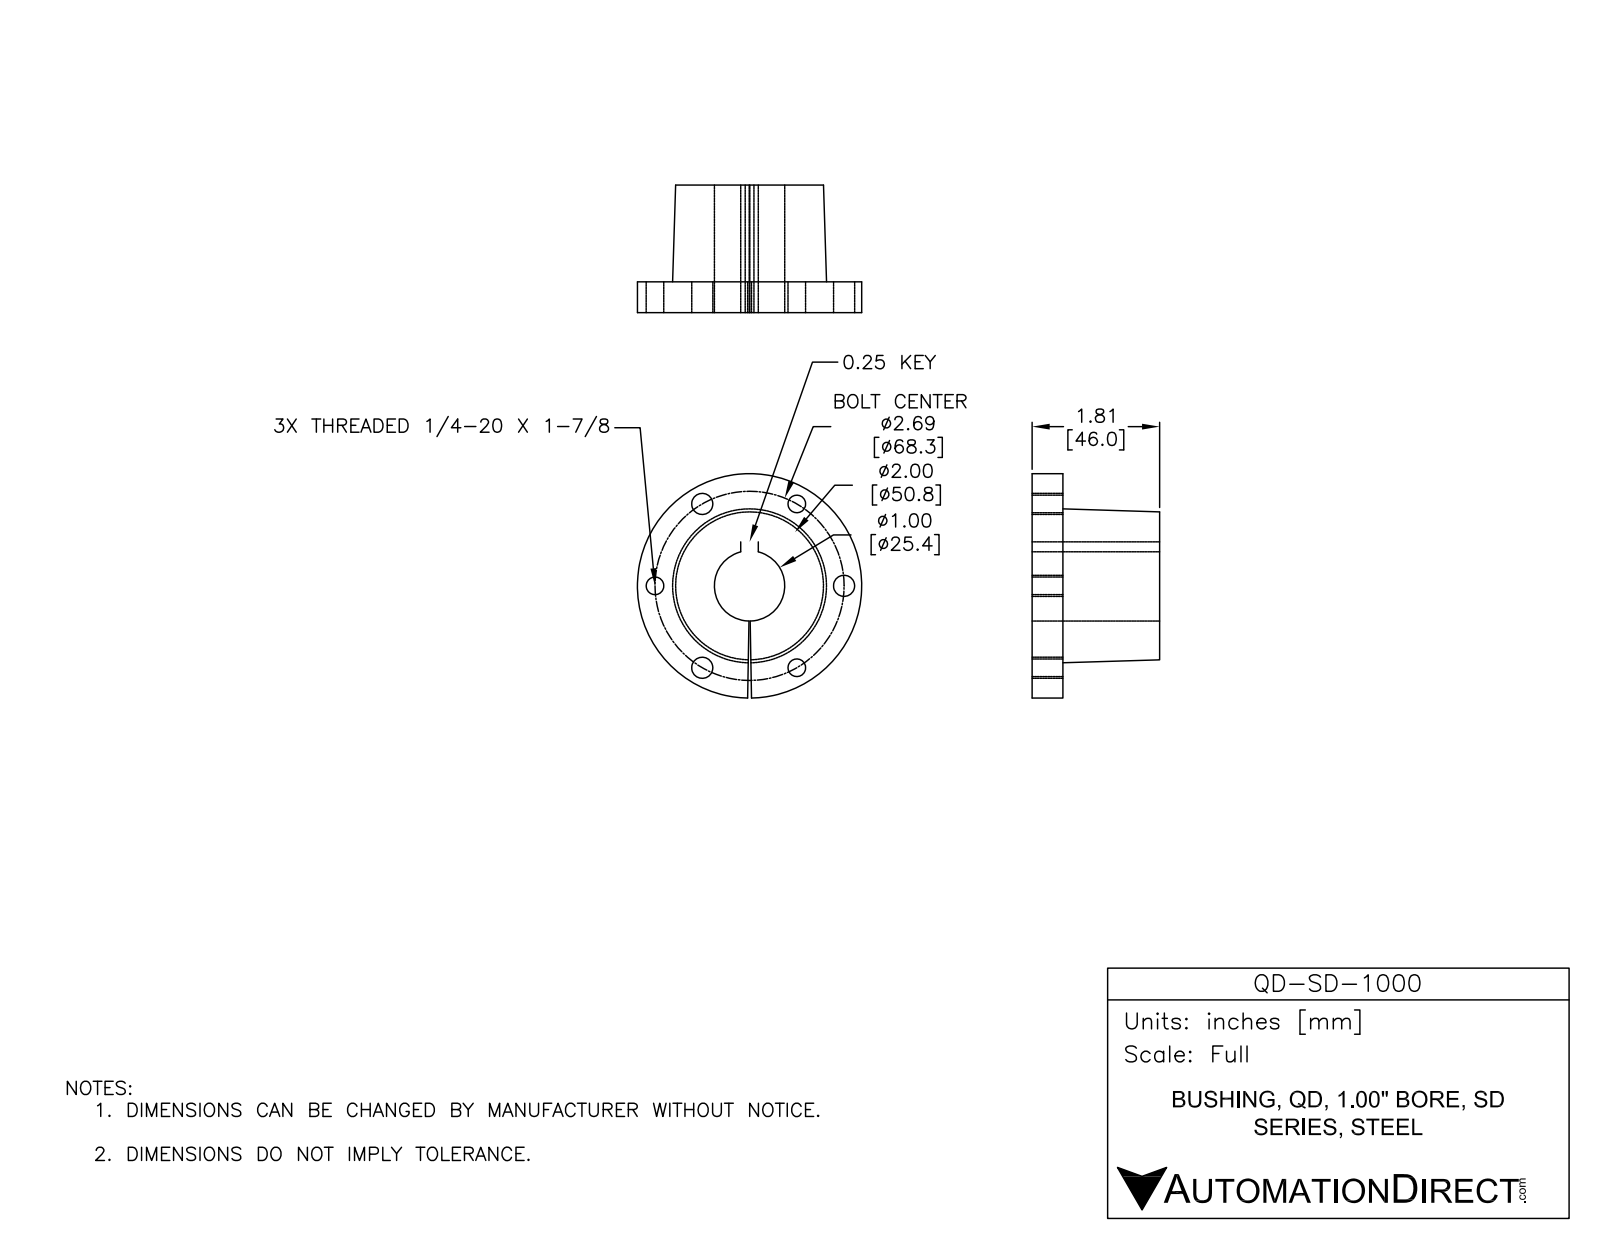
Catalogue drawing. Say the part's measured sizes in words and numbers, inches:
The part is named "QD-SD-1000". Its 3-D file was written by "SolidWorks 2014 (AUTOMOTIVE_DESIGN)". It is 1 solid with 29 faces: 8 planar, 18 cylindrical and 3 other. Overall it measures 3.188 by 3.187 by 1.813 inches. Its volume is 6.787 cubic inches and its surface area 37.73 square inches. Round holes: 3 of diameter 0.25, 3 of diameter 0.3, 1 of diameter 1. Round bosses or shafts: 1 of diameter 3.187. The main face-to-face distances are 0.437, 1.812, 1.375, 0.25. The hole center spacings are 1.344, 2.328, 1.344, 2.688, 2.687.
